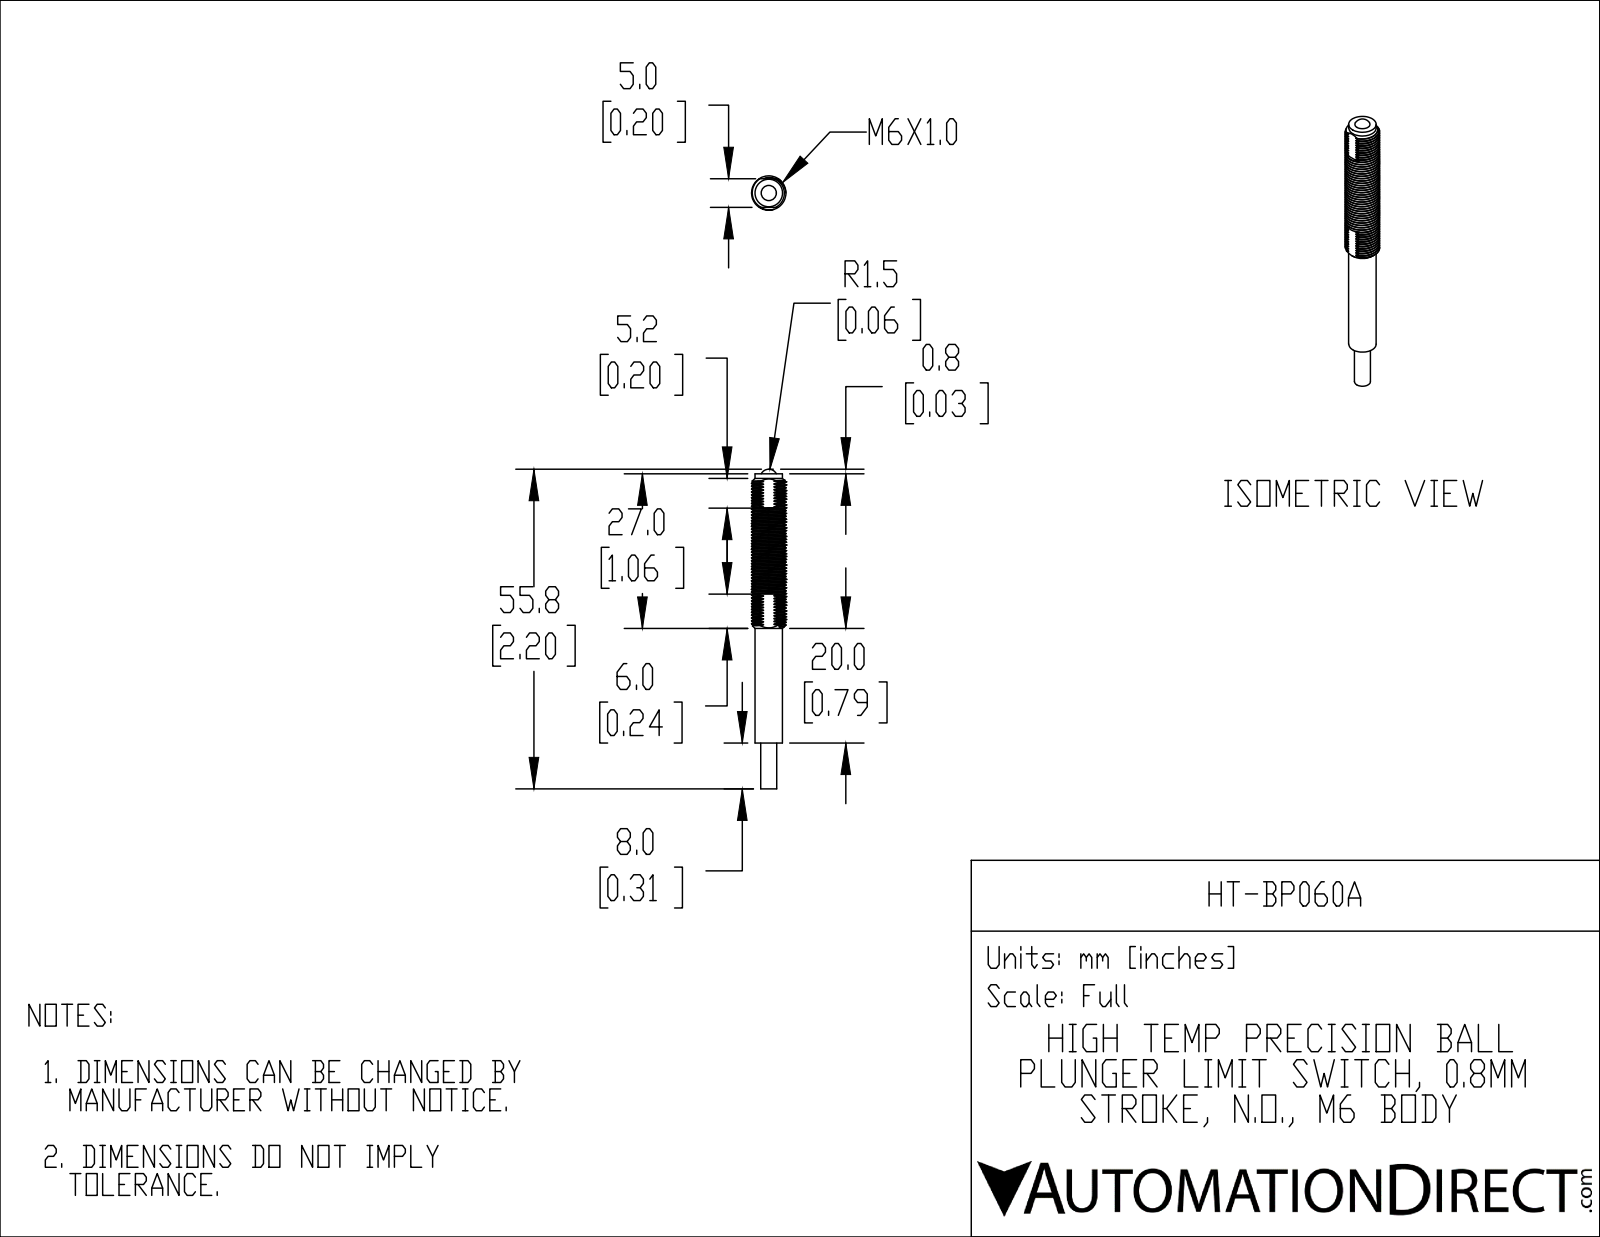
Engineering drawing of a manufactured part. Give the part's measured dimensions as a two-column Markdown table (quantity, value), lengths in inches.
| quantity | value |
| --- | --- |
| STEP written by | Spatial InterOp 3D (CONFIG_CONTROL_DESIGN) |
| units | inches |
| bodies | 1 solid, 254 faces (11 planar, 107 cylindrical, 136 other) |
| overall size | 2.197 × 0.236 × 0.236 |
| volume | 0.066 in³ |
| surface area | 1.872 in² |
| round bosses / shafts (diameter × count) | 0.236 × 1, 0.189 × 1, 0.11 × 1 |
| main face-to-face distances | 0.197, 1.85, 2.165, 0.315, 0.236, 1.614, 1.929, 0.827, 0.591, 1.024 |
